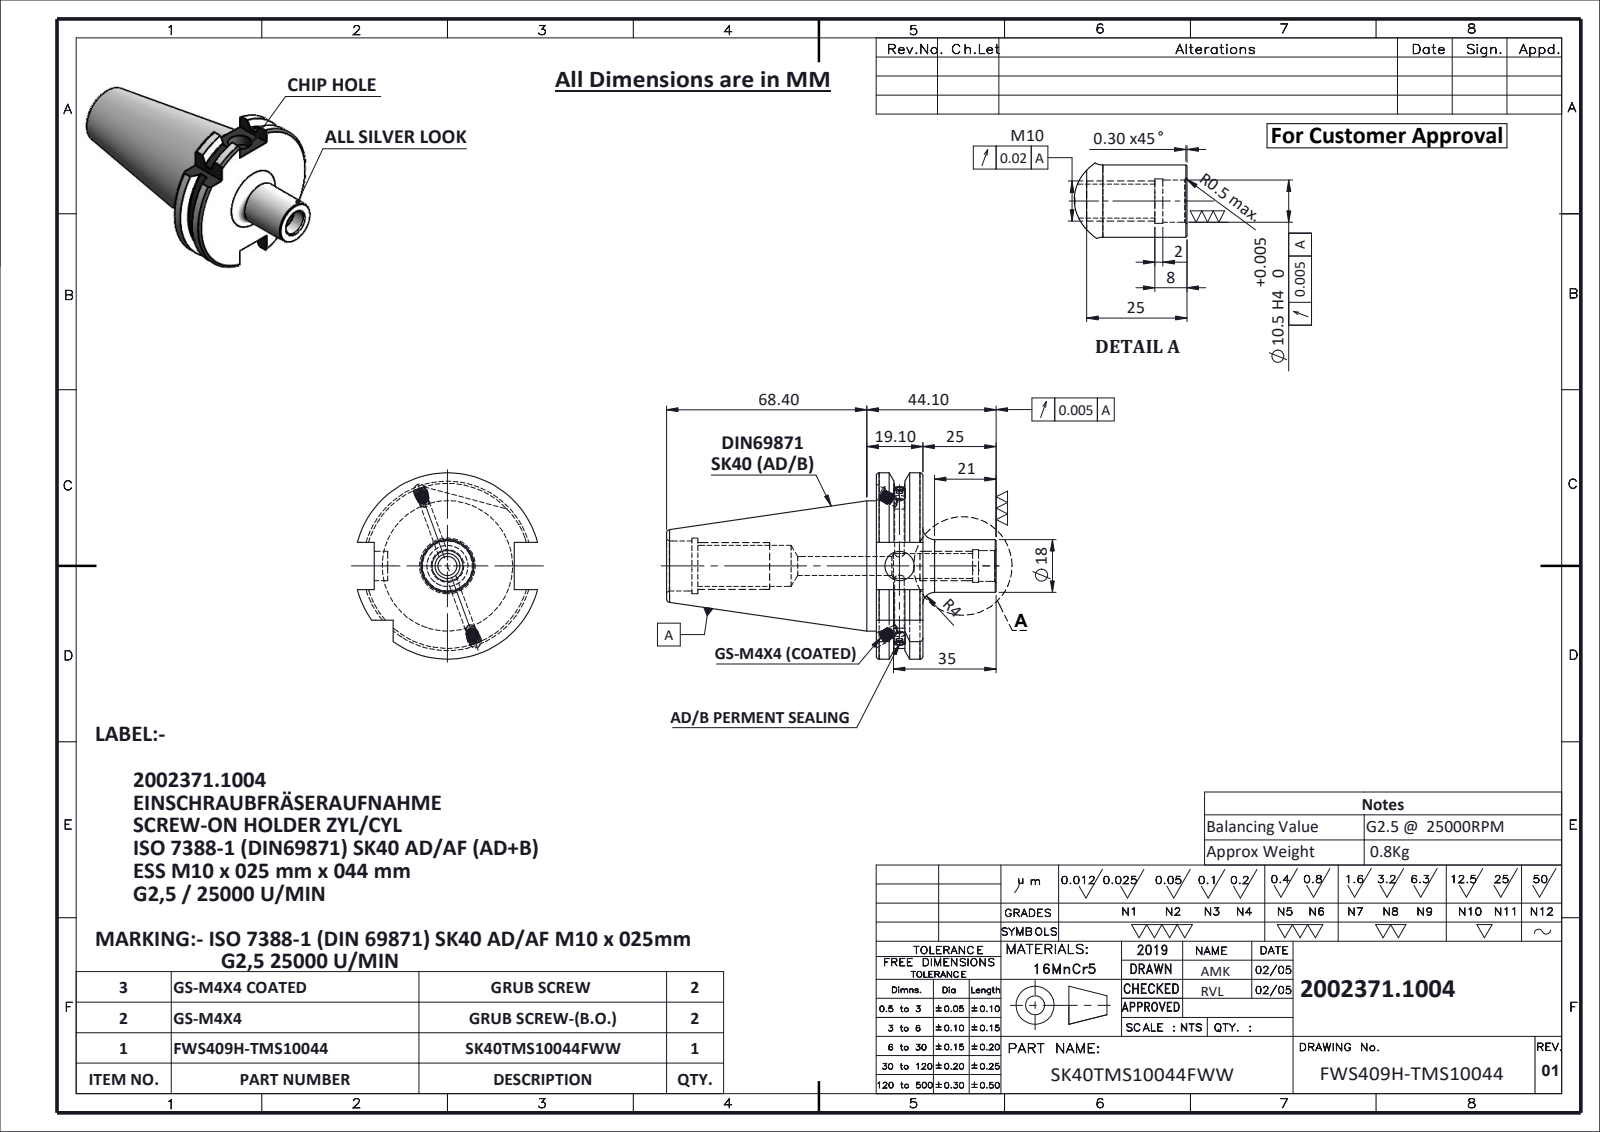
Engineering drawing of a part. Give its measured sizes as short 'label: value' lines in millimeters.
name: M4X4_DIN 913 - M4 x 4-N; GS-M4X4-COATING_DIN 913 - M4 x 4-N; FWS409H-TMS10044; SK40TMS10044FWW
written by: SolidWorks 2024 (CONFIG_CONTROL_DESIGN)
unit: mm
bodies: 5 solids, 242 faces (64 planar, 72 cylindrical, 106 other)
size: 112.5 × 63.55 × 61.48
volume: 108 371 mm³; area: 22 915 mm²
holes: 3× ⌀3.3, 2× ⌀4.5, 1× ⌀6.5, 1× ⌀8.5, 1× ⌀10, 1× ⌀10.5, 1× ⌀11.1, 1× ⌀14, 1× ⌀17, 1× ⌀19
bosses: 4× ⌀4, 2× ⌀2.9, 1× ⌀44.45, 1× ⌀18
rounds: 1× R28.12, 1× R31.77
face distances: 15.9, 16.1, 47.8, 71.6, 87.5, 112.5, 40.9, 25, 10.7, 60.9
